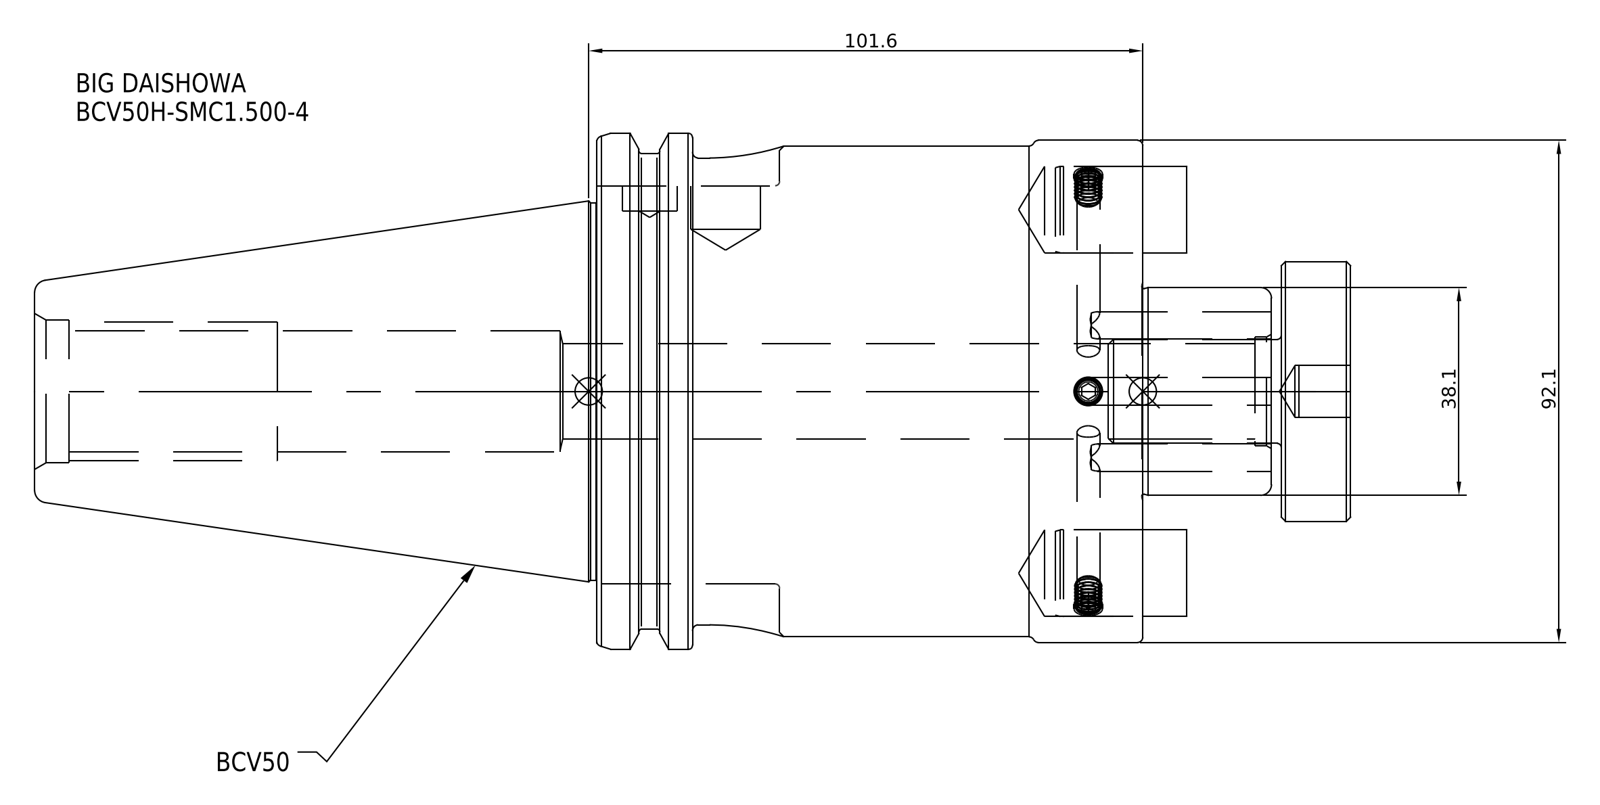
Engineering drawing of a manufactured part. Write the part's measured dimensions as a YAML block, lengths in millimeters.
part_name: "BCV50H-SMC1_500-4"
step_written_by: "SolidWorks 2021 (CONFIG_CONTROL_DESIGN)"
units: millimeters
bodies: {solids: 1, faces: 38, planar: 18, cylindrical: 14, other: 6}
overall_size: [211.28, 98.43, 98.43]
volume: 903706
surface_area: 65519
round_holes:
  - {diameter: 17.5, count: 1}
round_bosses_or_shafts:
  - {diameter: 98.43, count: 1}
  - {diameter: 92.1, count: 1}
  - {diameter: 91.29, count: 1}
  - {diameter: 90, count: 1}
  - {diameter: 69.85, count: 1}
face_to_face_distances: [100.1, 203.2, 103.1, 82.55, 17.55, 120.65, 15.88, 8.08, 90.63, 108.18]
